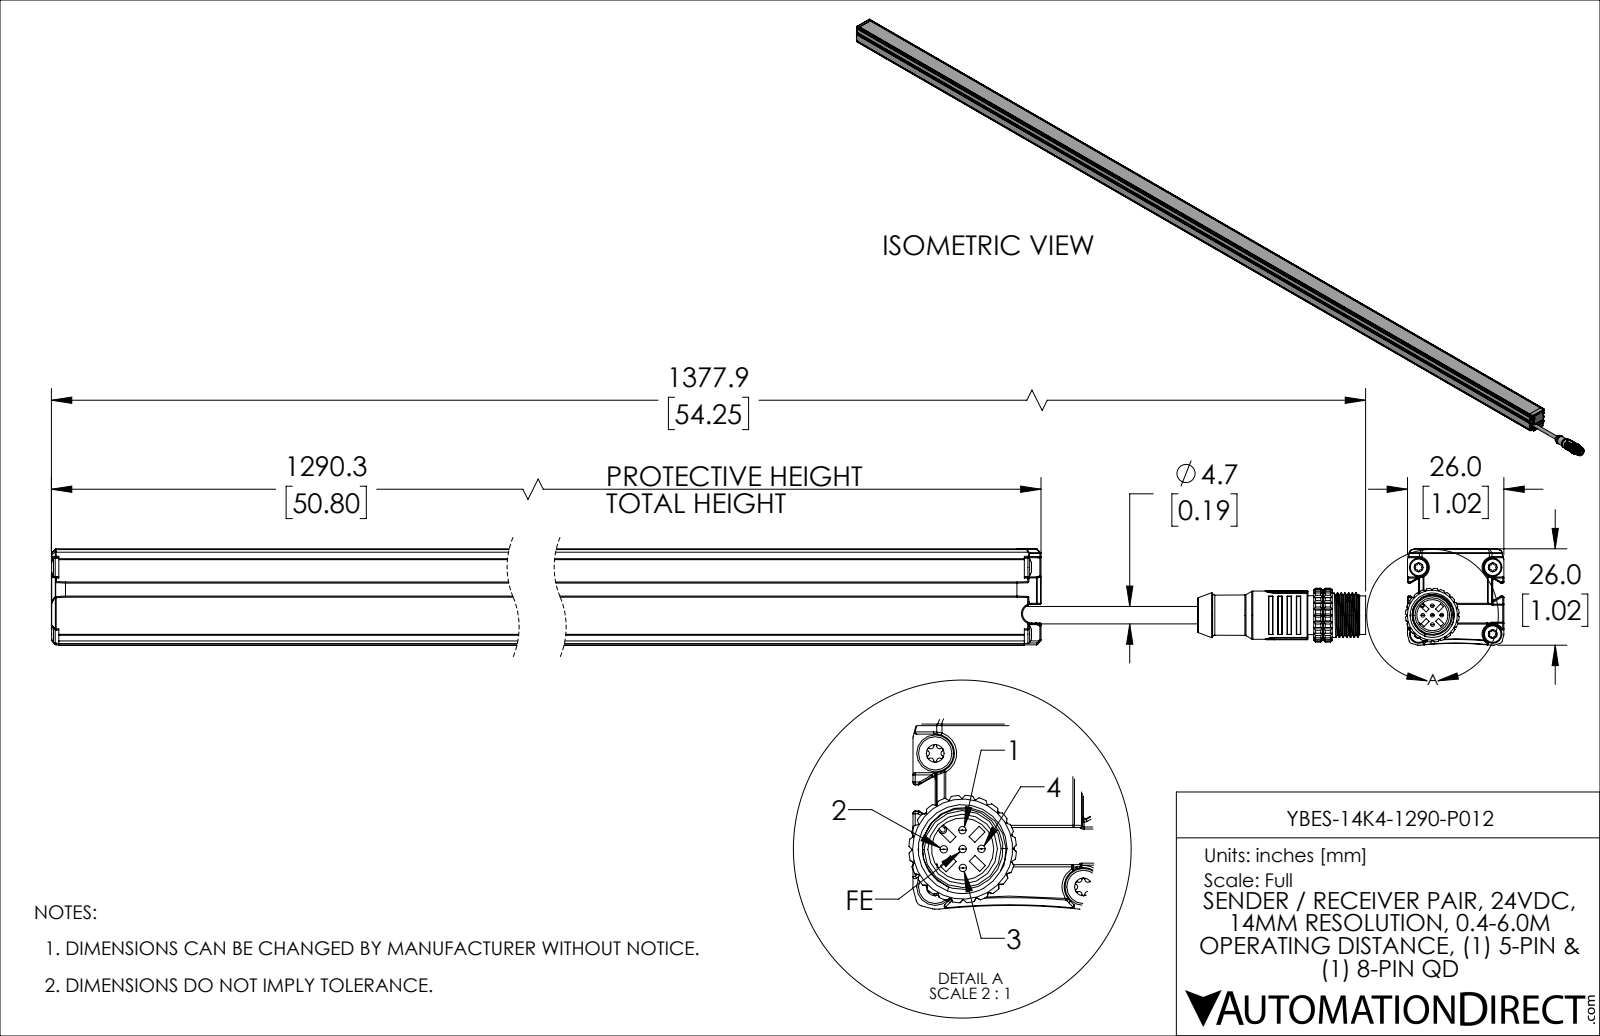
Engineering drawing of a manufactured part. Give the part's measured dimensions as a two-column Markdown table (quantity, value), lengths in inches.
| quantity | value |
| --- | --- |
| part name | YBES-14K4-1290-P012_REV1 |
| STEP written by | SolidWorks 2019 (AUTOMOTIVE_DESIGN) |
| units | inches |
| bodies | 2 solids, 1743 faces (549 planar, 719 cylindrical, 475 other) |
| overall size | 54.248 × 1.045 × 1.024 |
| volume | 18.31 in³ |
| surface area | 508.2 in² |
| round holes (diameter × count) | 0.094 × 4, 0.1 × 4, 0.146 × 4, 0.197 × 4, 0.189 × 1, 0.232 × 1, 0.331 × 1 |
| round bosses / shafts (diameter × count) | 0.039 × 5, 0.126 × 4, 0.098 × 4, 0.051 × 4, 0.059 × 2, 0.531 × 1, 0.512 × 1, 0.472 × 1 |
| partial cylindrical surfaces (radius × count) | 0.008 × 153, 0.012 × 115, 0.008 × 24, 0.015 × 24, 0.039 × 18, 0.016 × 16, 0.006 × 10, 0.02 × 7 |
| main face-to-face distances | 0.118, 0.059, 0.071, 0.835, 1.024, 0.717, 0.047, 0.016, 0.906, 0.189 |
| hole center spacings | 0.709, 0.787, 1.059, 0.248, 0.528, 0.672, 0.819 |
